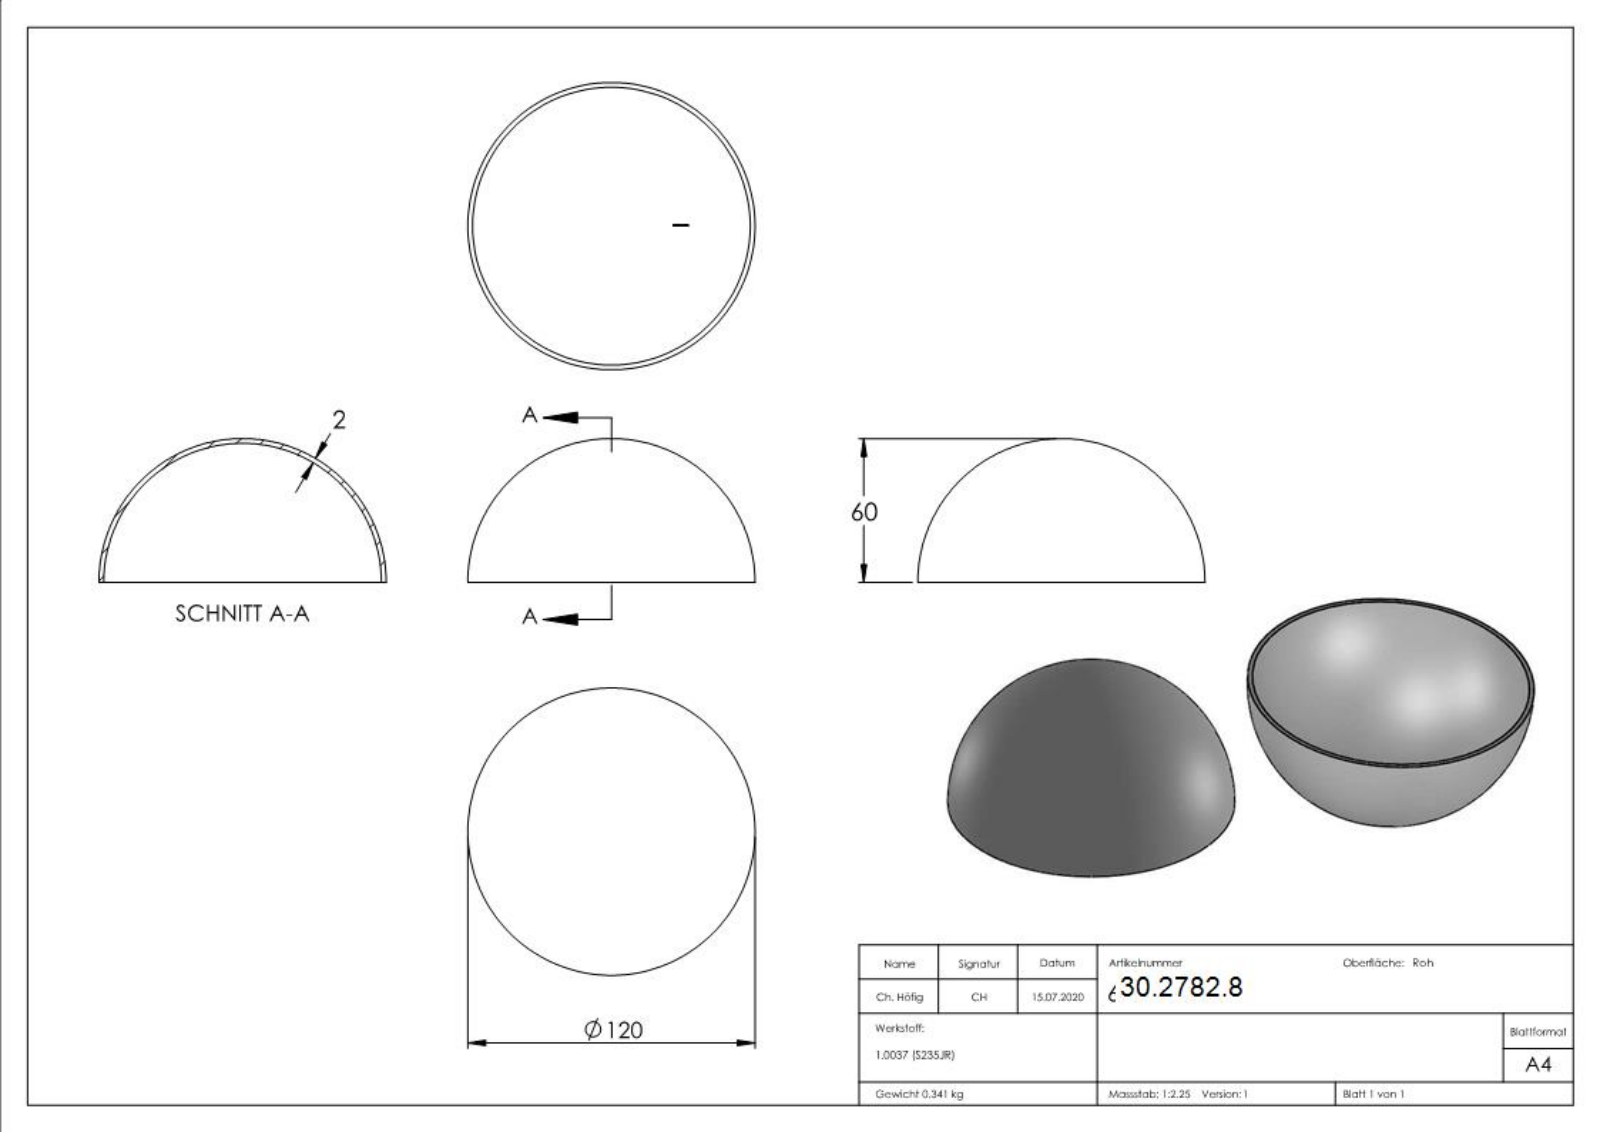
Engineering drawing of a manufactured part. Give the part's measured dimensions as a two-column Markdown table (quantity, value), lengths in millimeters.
| quantity | value |
| --- | --- |
| part name | 620120 |
| STEP written by | SolidWorks 2018 (CONFIG_CONTROL_DESIGN) |
| units | millimeters |
| bodies | 1 solid, 185 faces (76 planar, 0 cylindrical, 109 other) |
| overall size | 120 × 120 × 60 |
| volume | 43 748 mm³ |
| surface area | 44 501 mm² |
| main face-to-face distances | 1.19, 0.55, 0.5, 0.81, 0.66, 3.1, 1.74, 0.53, 1.31, 0.45 |
